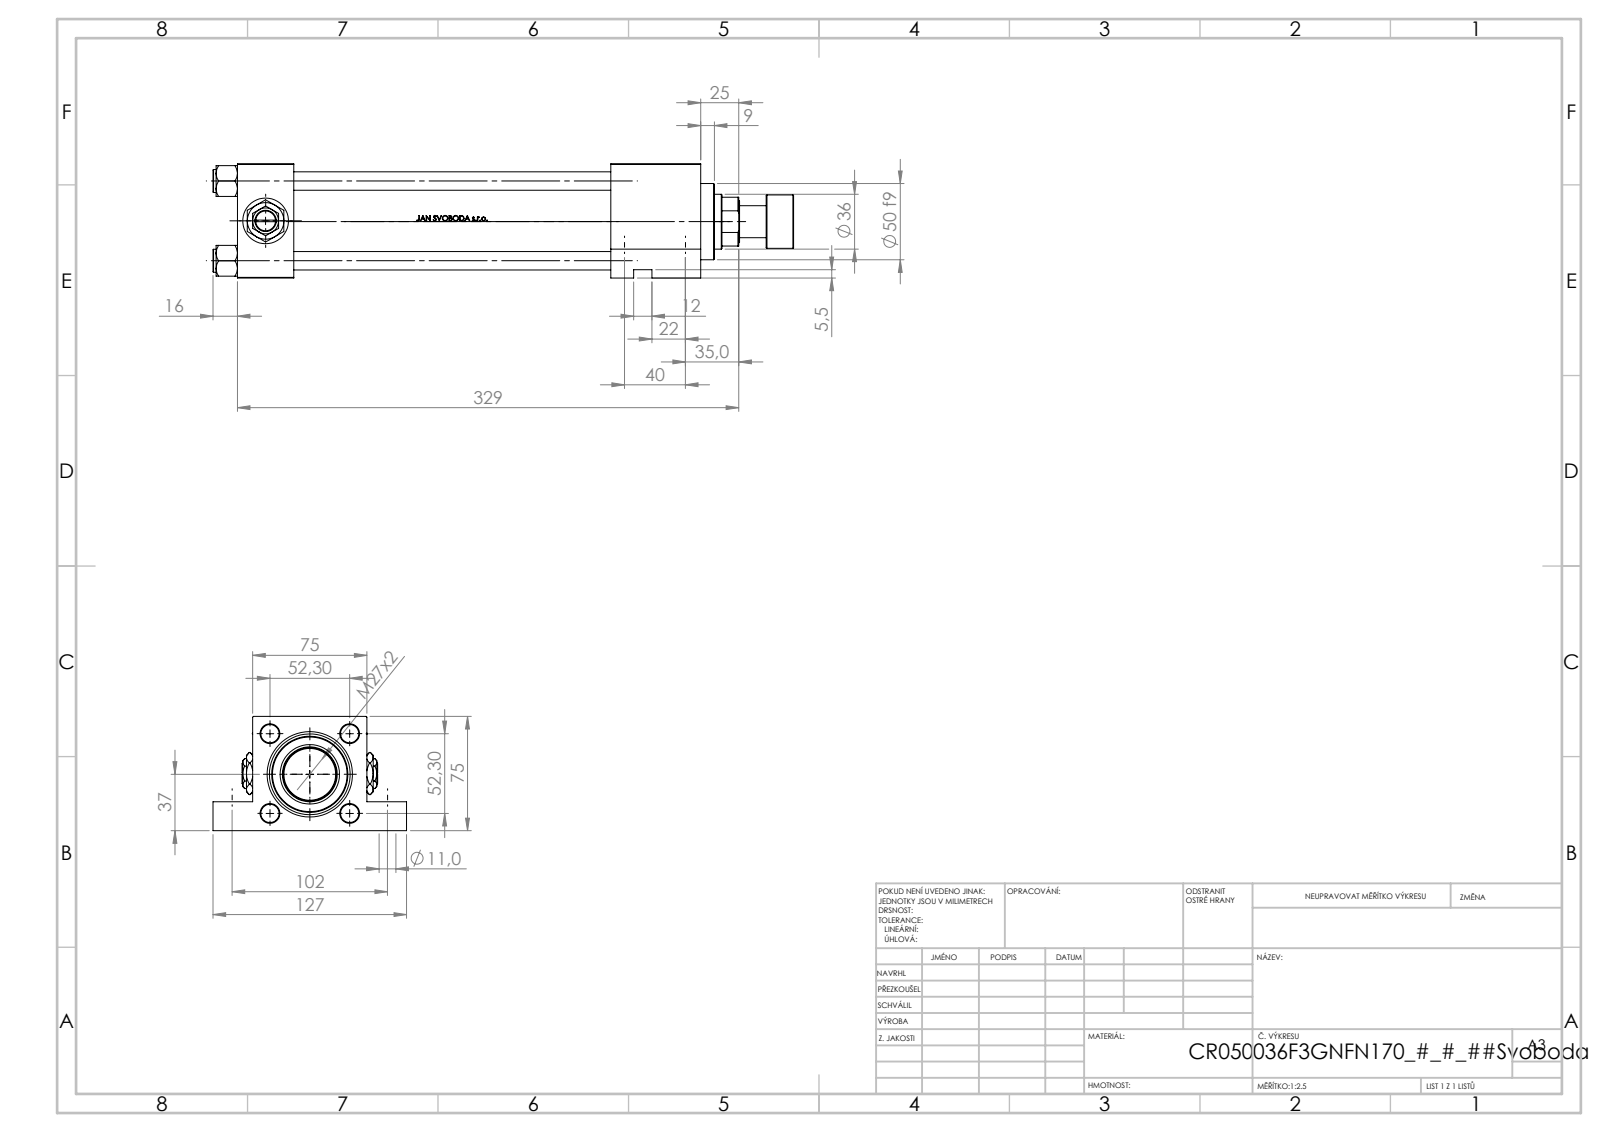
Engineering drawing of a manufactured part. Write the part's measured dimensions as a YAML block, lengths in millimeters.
part_name: "V215CR_ROD_END_F; Zatka_pro_OIL_PORT; V215CR_VCP_F; V215CR_F_Body (+3 more)"
step_written_by: "SolidWorks 2019 (CONFIG_CONTROL_DESIGN)"
units: millimeters
bodies: {solids: 14, faces: 1201, planar: 485, cylindrical: 130, other: 586}
overall_size: [381, 127, 75]
volume: 1059000
surface_area: 262716
round_holes:
  - {diameter: 11, count: 4}
  - {diameter: 12, count: 4}
  - {diameter: 7, count: 2}
  - {diameter: 20.96, count: 2}
  - {diameter: 30, count: 2}
  - {diameter: 25.5, count: 1}
  - {diameter: 36, count: 1}
  - {diameter: 39, count: 1}
  - {diameter: 41, count: 1}
  - {diameter: 53, count: 1}
round_bosses_or_shafts:
  - {diameter: 15, count: 4}
  - {diameter: 56, count: 1}
  - {diameter: 50, count: 1}
  - {diameter: 35, count: 1}
  - {diameter: 21, count: 1}
face_to_face_distances: [75, 37, 245, 208, 59, 304, 267, 19, 56, 26]
hole_center_spacings: [52.3, 36.63, 37.34, 40, 73.96, 102, 109.56, 243.5]
